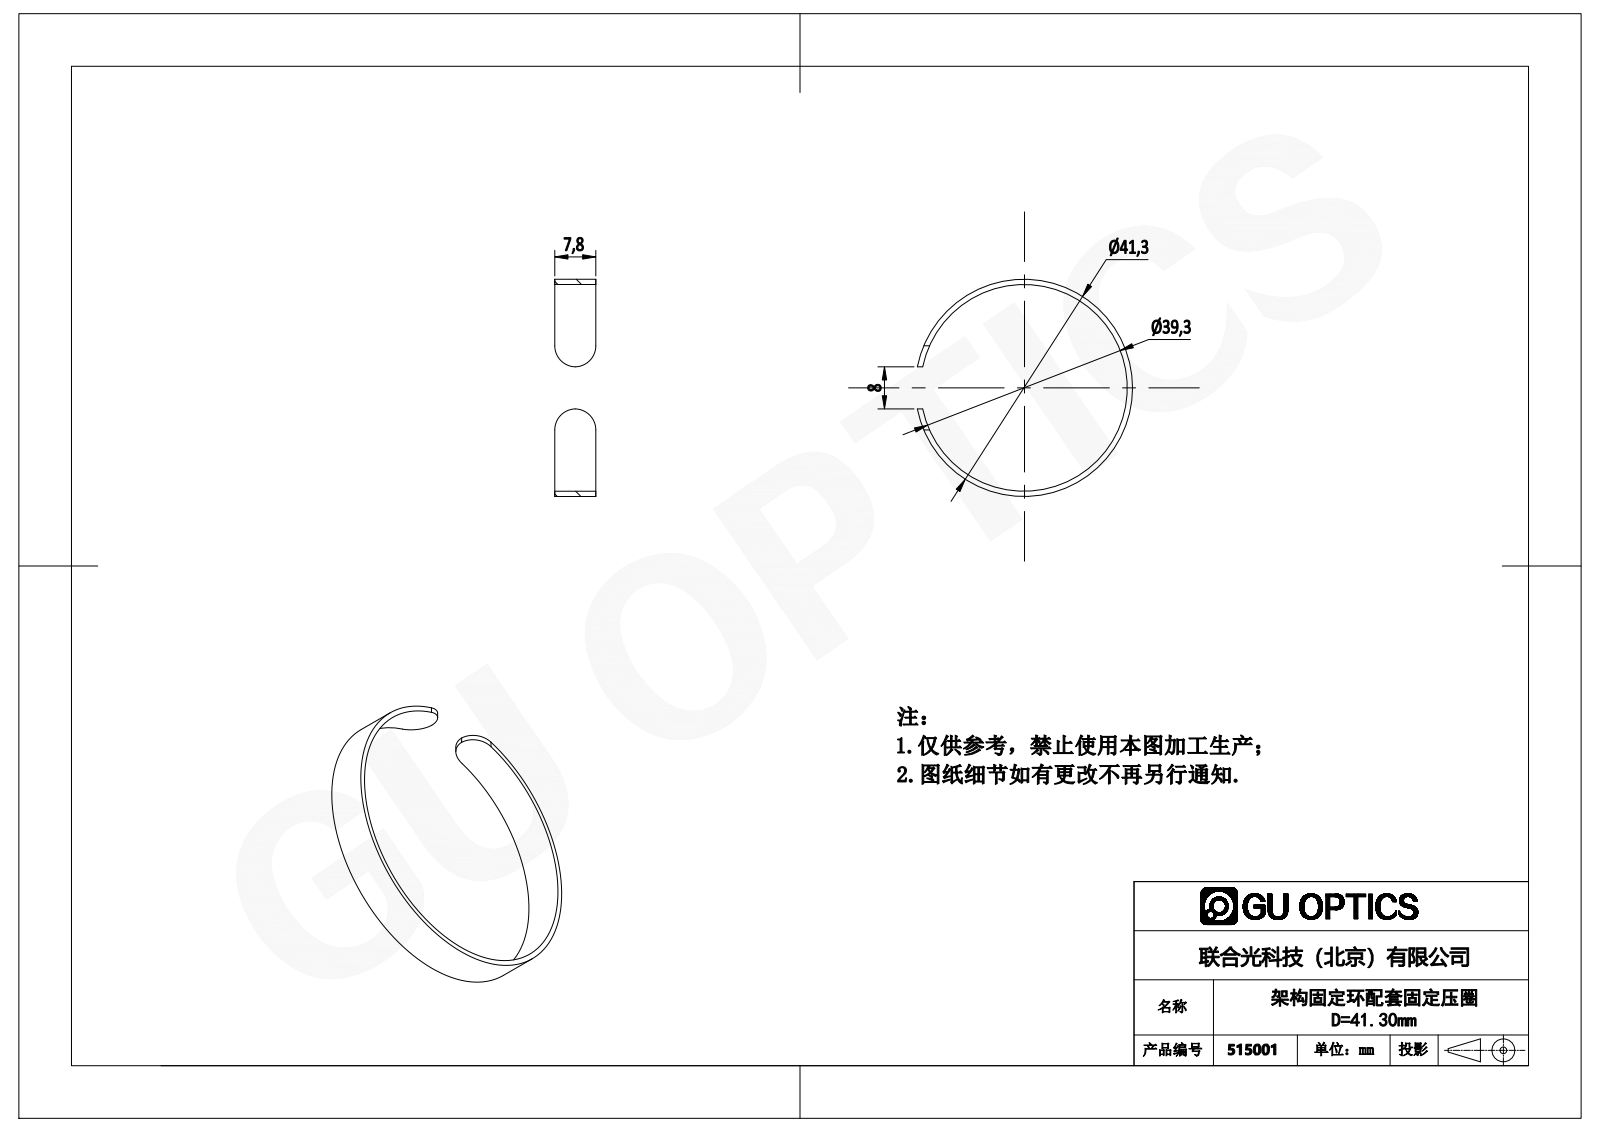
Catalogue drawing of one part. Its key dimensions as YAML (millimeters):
part_name: "515001"
step_written_by: "SolidWorks 2016 (CONFIG_CONTROL_DESIGN)"
units: millimeters
bodies: {solids: 1, faces: 12, planar: 2, cylindrical: 10, other: 0}
overall_size: [41.3, 40.91, 7.8]
volume: 911
surface_area: 2067
round_holes:
  - {diameter: 39.3, count: 1}
round_bosses_or_shafts:
  - {diameter: 41.3, count: 1}
partial_cylinders:
  - {radius: 4, count: 4}
face_to_face_distances: [7.8]
